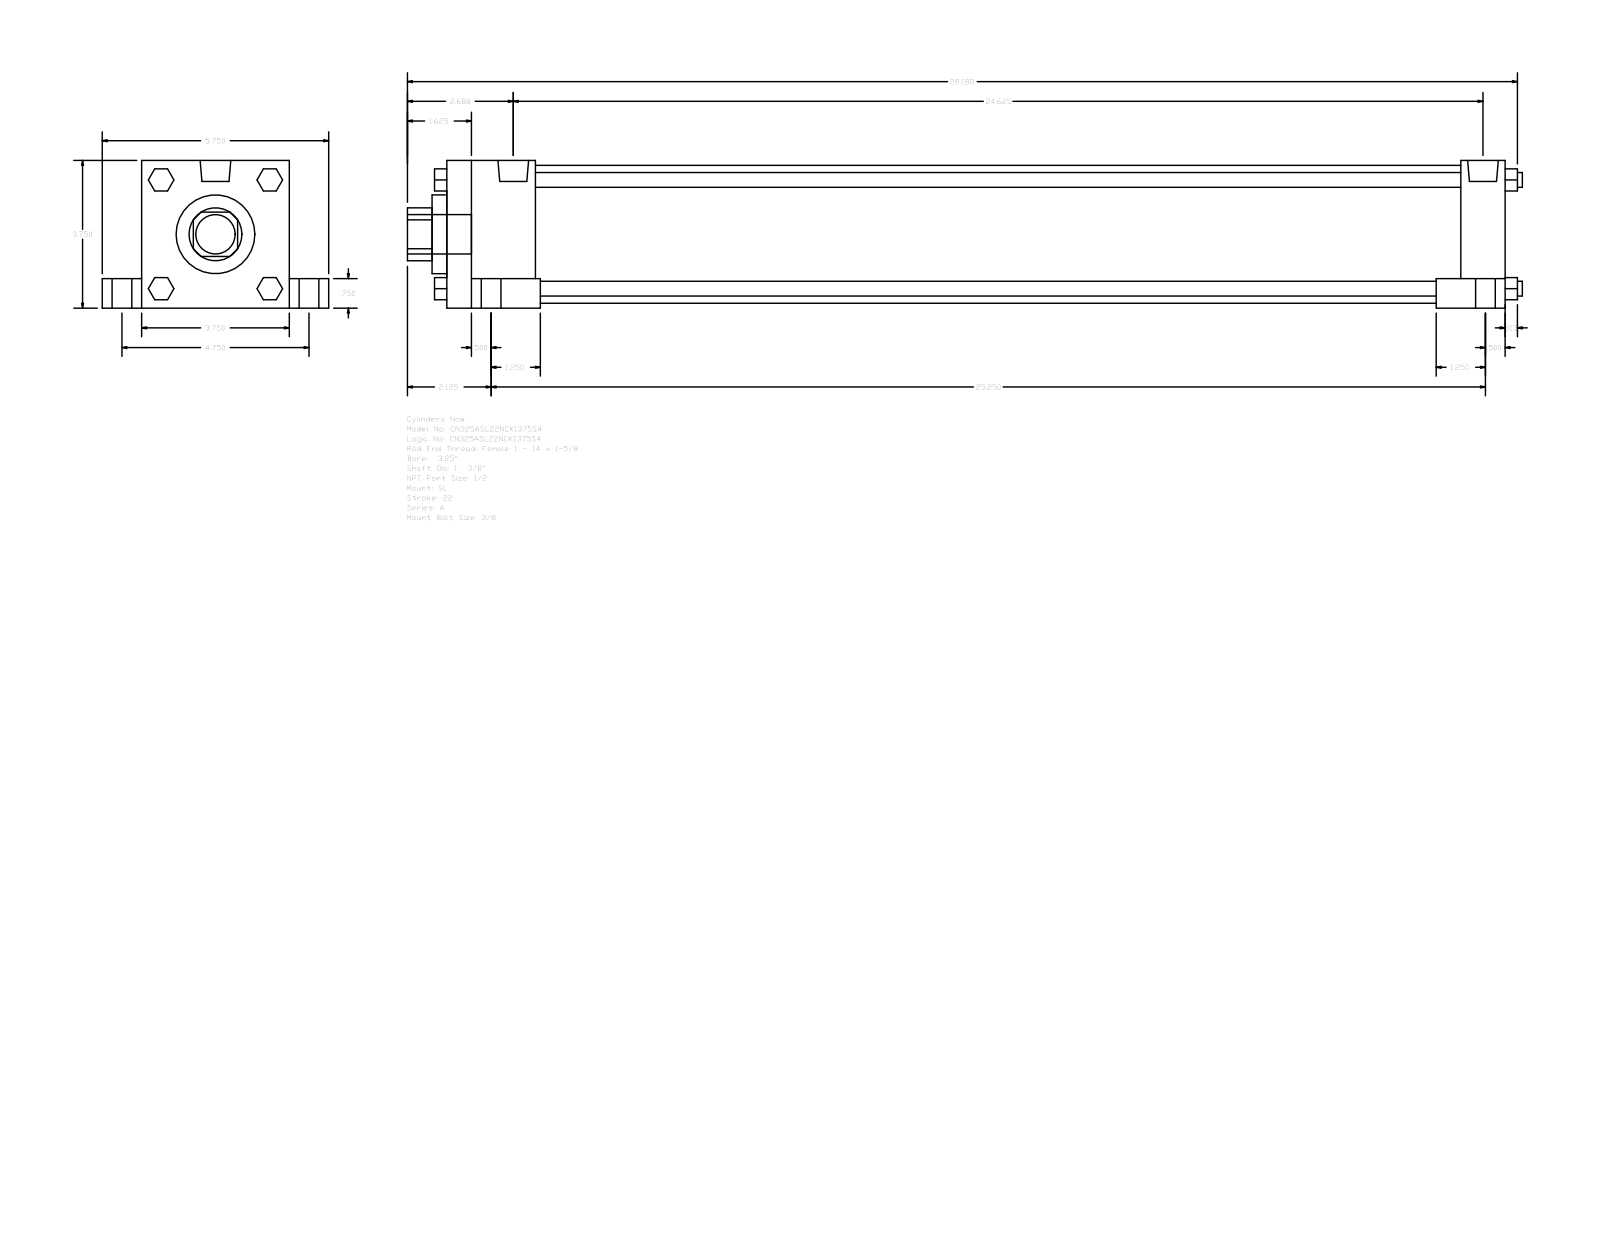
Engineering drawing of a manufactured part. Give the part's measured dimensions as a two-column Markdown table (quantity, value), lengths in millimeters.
| quantity | value |
| --- | --- |
| part name | A_SL__0325_1.375 |
| STEP written by | GSSL Pune (CONFIG_CONTROL_DESIGN) |
| units | millimeters |
| bodies | 0 solids, 150 faces (114 planar, 36 cylindrical, 0 other) |
| overall size | 719.14 × 146.05 × 95.25 |
| round holes (diameter × count) | 34.92 × 1, 50.8 × 1, 88.9 × 1 |
| round bosses / shafts (diameter × count) | 19.05 × 4, 12.7 × 4, 9.53 × 4, 8.73 × 4, 19.77 × 2, 25.4 × 1 |
| partial cylindrical surfaces (radius × count) | 17.06 × 1 |
| main face-to-face distances | 95.24, 682.62, 25.41, 120.65, 19.05, 76.19, 15.87, 28.57, 57.15, 654.05 |
